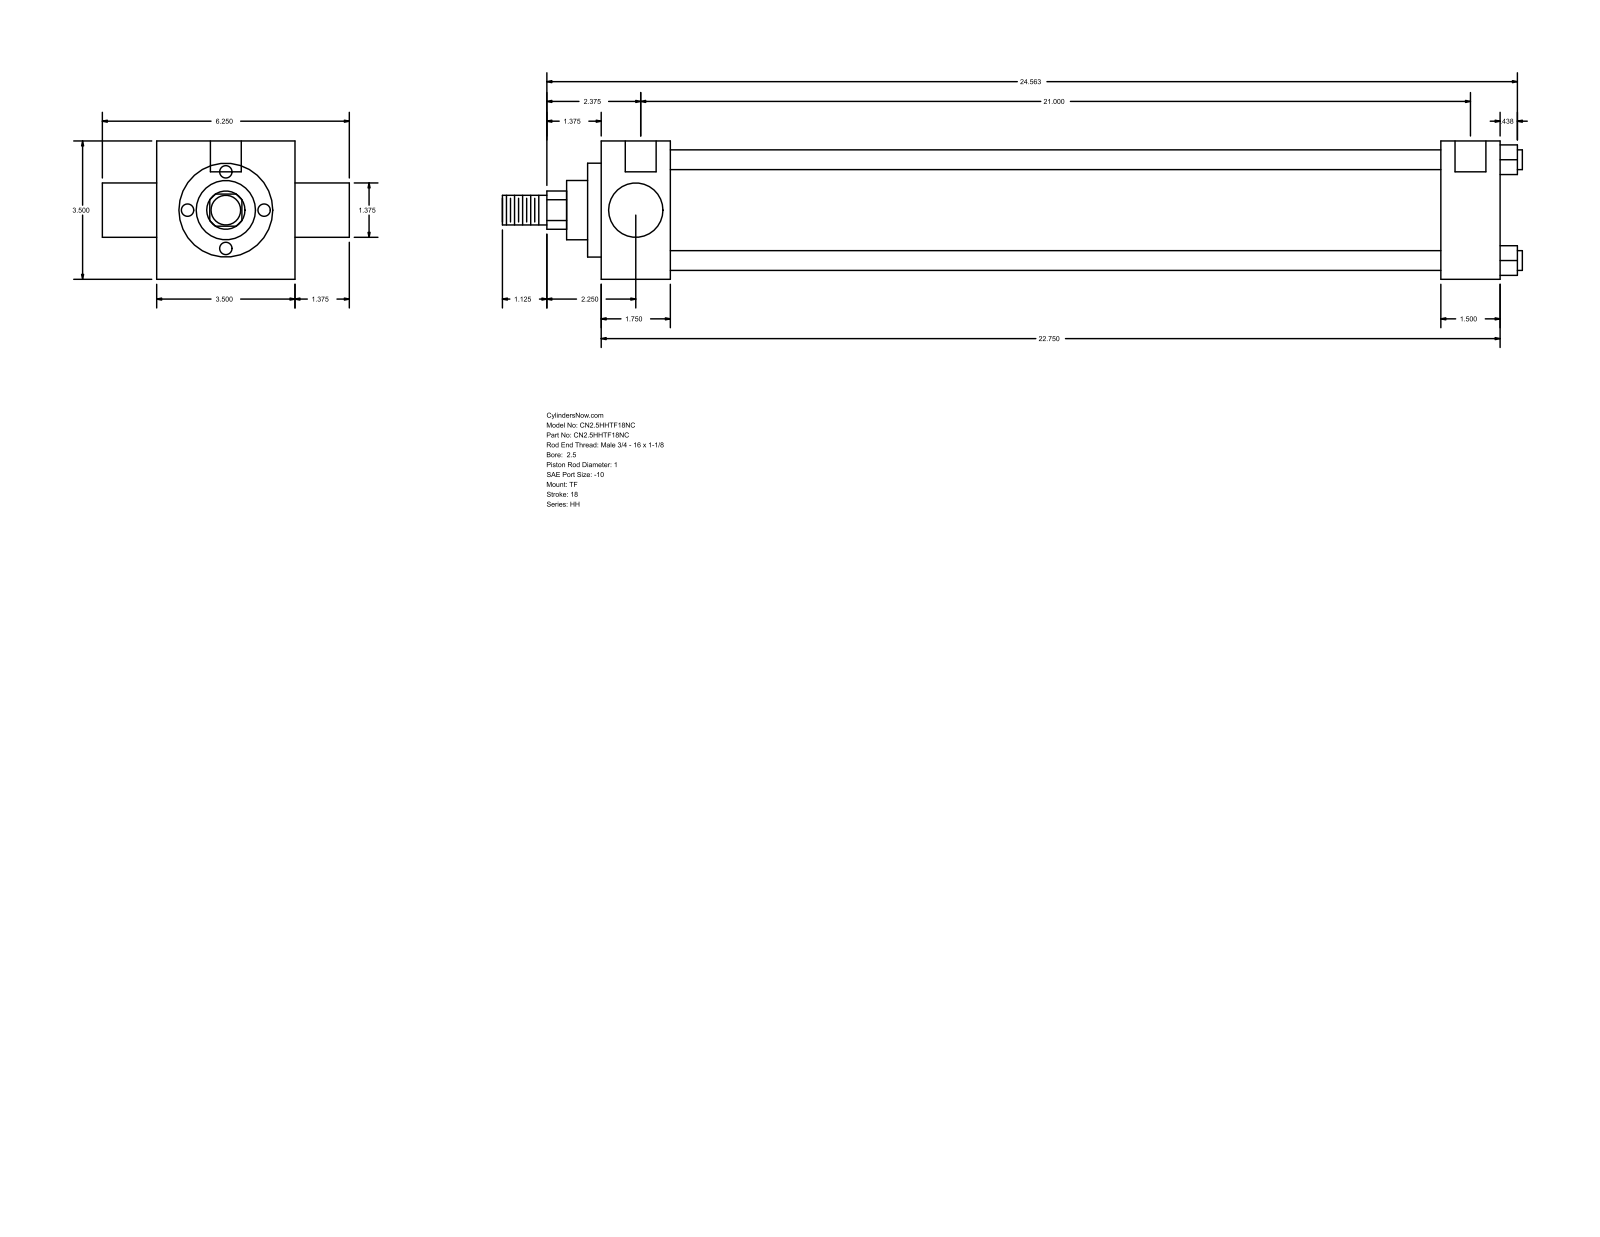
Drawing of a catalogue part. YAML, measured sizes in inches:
part_name: "HH_TF__0250_1"
step_written_by: "GSSL Pune (CONFIG_CONTROL_DESIGN)"
units: inches
bodies: {solids: 0, faces: 86, planar: 61, cylindrical: 25, other: 0}
overall_size: [25.813, 6.25, 3.5]
round_holes:
  - {diameter: 0.219, count: 3}
  - {diameter: 0.781, count: 2}
round_bosses_or_shafts:
  - {diameter: 0.5, count: 4}
  - {diameter: 2.875, count: 1}
  - {diameter: 2.375, count: 1}
  - {diameter: 1.5, count: 1}
  - {diameter: 1.375, count: 1}
  - {diameter: 1, count: 1}
  - {diameter: 0.75, count: 1}
partial_cylinders:
  - {radius: 0.484, count: 1}
face_to_face_distances: [3.5, 22.75, 1.5, 1.75, 21, 21.25, 19.5, 1.375, 4.875, 0.344]
hole_center_spacings: [0.062, 0.063, 21, 21.062, 21.063, 21.125]
